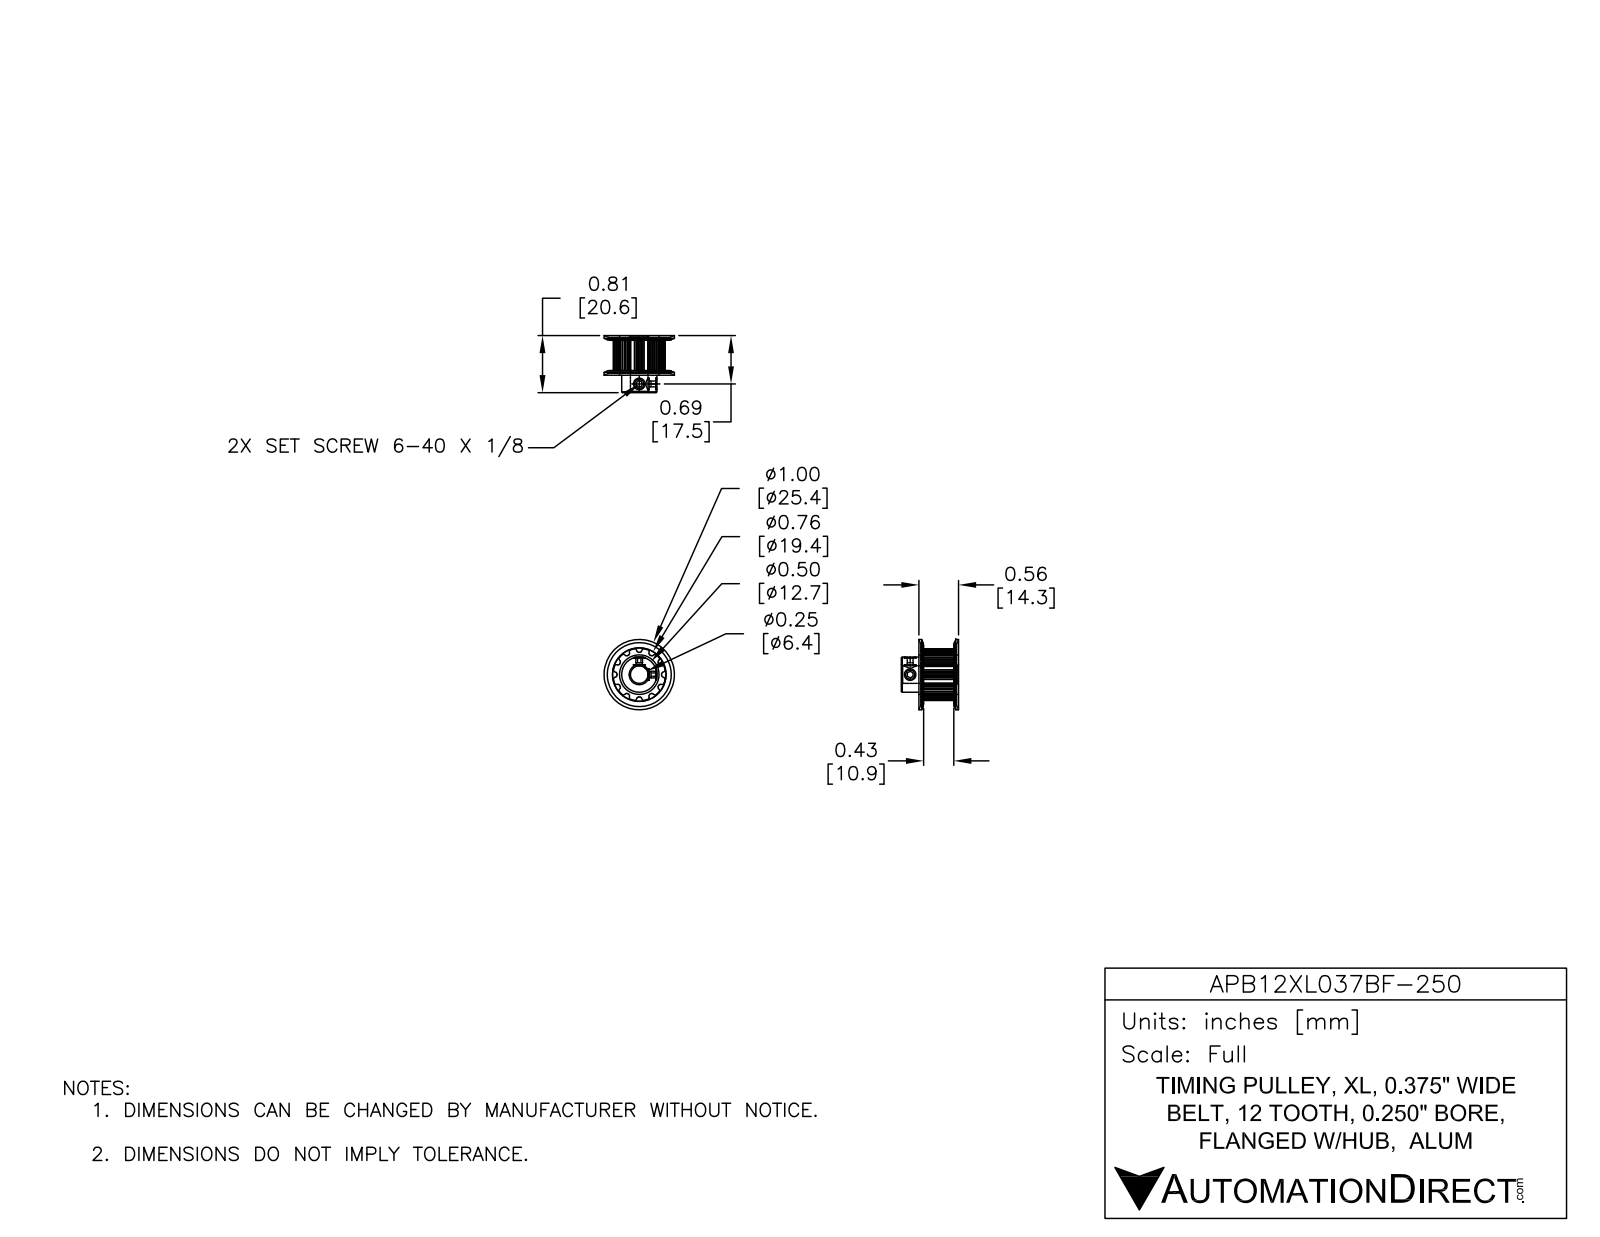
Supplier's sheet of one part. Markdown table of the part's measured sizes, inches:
| quantity | value |
| --- | --- |
| part name | APB12XL037BF-250 |
| STEP written by | SolidWorks 2014 (AUTOMOTIVE_DESIGN) |
| units | inches |
| bodies | 1 solid, 142 faces (42 planar, 78 cylindrical, 22 other) |
| overall size | 1 × 1 × 0.813 |
| volume | 0.237 in³ |
| surface area | 4.922 in² |
| round holes (diameter × count) | 0.088 × 2, 0.25 × 1 |
| round bosses / shafts (diameter × count) | 0.5 × 1 |
| partial cylindrical surfaces (radius × count) | 0.015 × 48, 0.317 × 1 |
| main face-to-face distances | 0.495, 0.033, 0.744, 0.528, 0.221, 0.813, 0.78, 0.285, 0.065, 0.032 |
